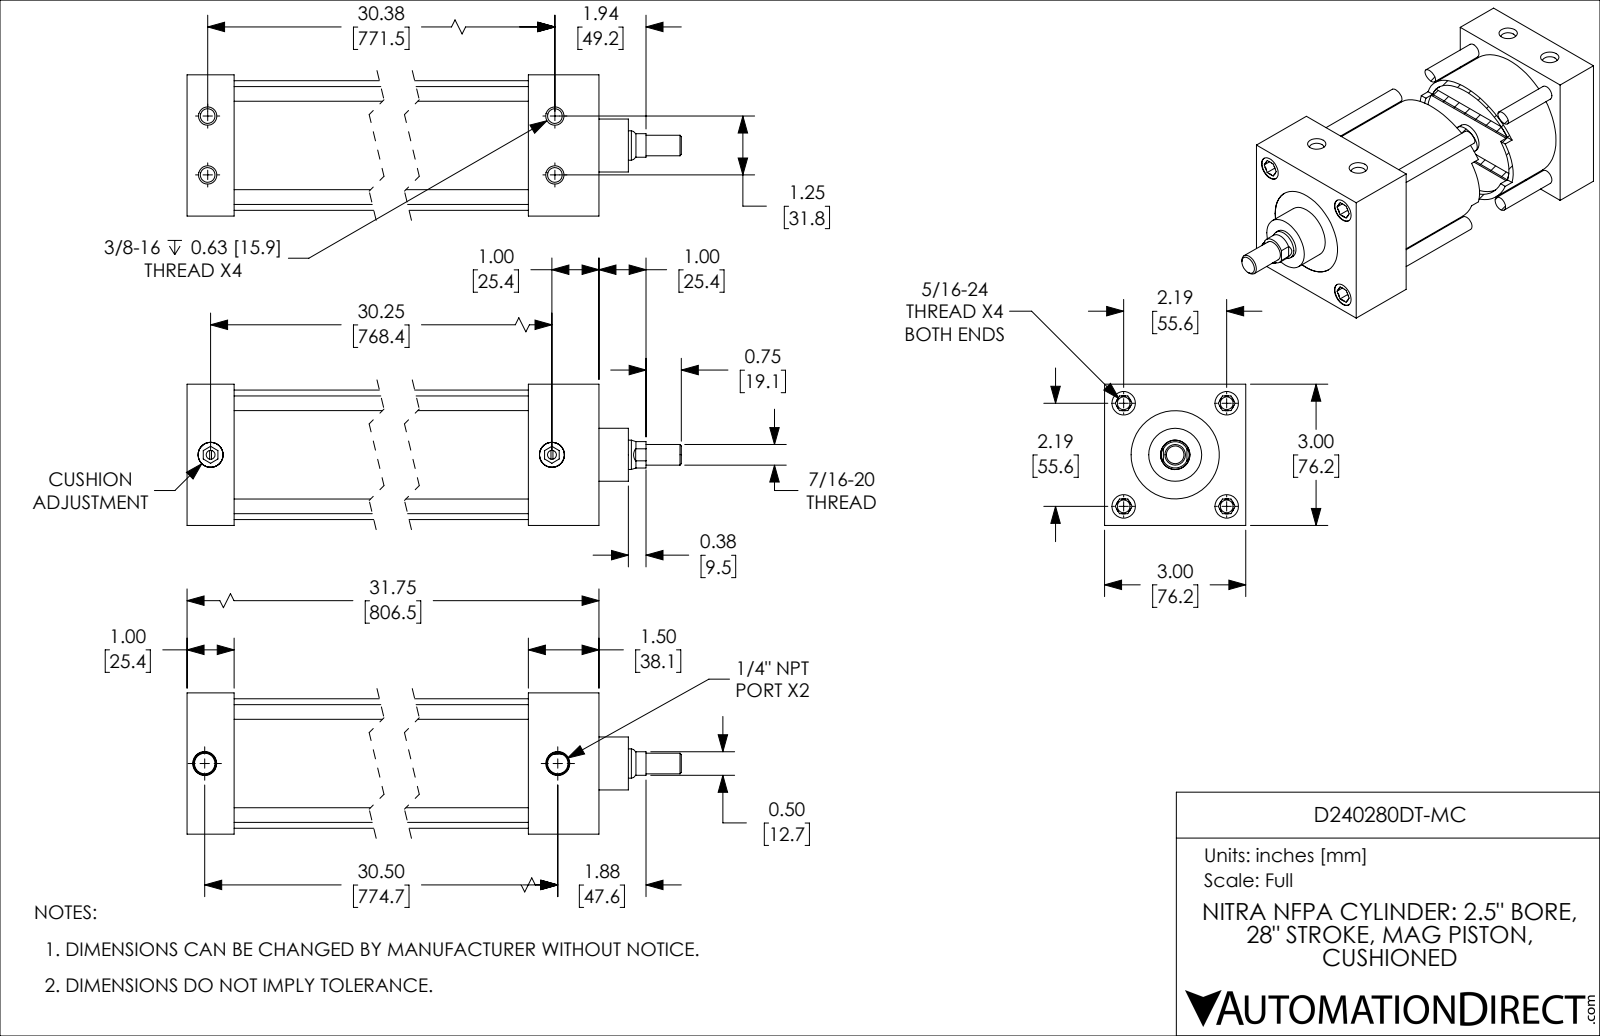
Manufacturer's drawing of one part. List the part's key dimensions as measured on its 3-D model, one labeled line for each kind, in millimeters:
Part name (STEP PRODUCT): D240280DT-MC_PISTON_KK1; D240280DT-MC; D240280DT-MC_BODY; D240280DT-MC_CUSHION
STEP written by: SolidWorks 2019 (CONFIG_CONTROL_DESIGN)
Units: millimetres
Bodies: 4 solids, 248 faces (90 planar, 78 cylindrical, 80 other)
Overall size (bounding box): 850.9 × 76.2 × 76.2
Volume: 1 245 000 mm³ · Surface area: 490 900 mm²
Round holes (diameter × count): ⌀6.9 ×4, ⌀8 ×4, ⌀12.7 ×4, ⌀4.8 ×2, ⌀11.1 ×2, ⌀13.5 ×2, ⌀15.9 ×1, ⌀47.6 ×1, ⌀63.5 ×1
Round bosses / shafts (diameter × count): ⌀7.9 ×4, ⌀13.5 ×2, ⌀69.9 ×1, ⌀63.5 ×1, ⌀28.6 ×1, ⌀15.8 ×1, ⌀11.1 ×1
Partial cylindrical surfaces — rounded edges, fillets, slot ends (radius × count): R7.1 ×1
Main face-to-face distances: 76.2, 25.4, 768.4, 743, 806.5, 781.1, 38.1, 31.8, 57.2, 711.2
Hole centre spacings: 39.3, 55.6, 773.3, 16, 16, 31.8, 78.7, 771.5
